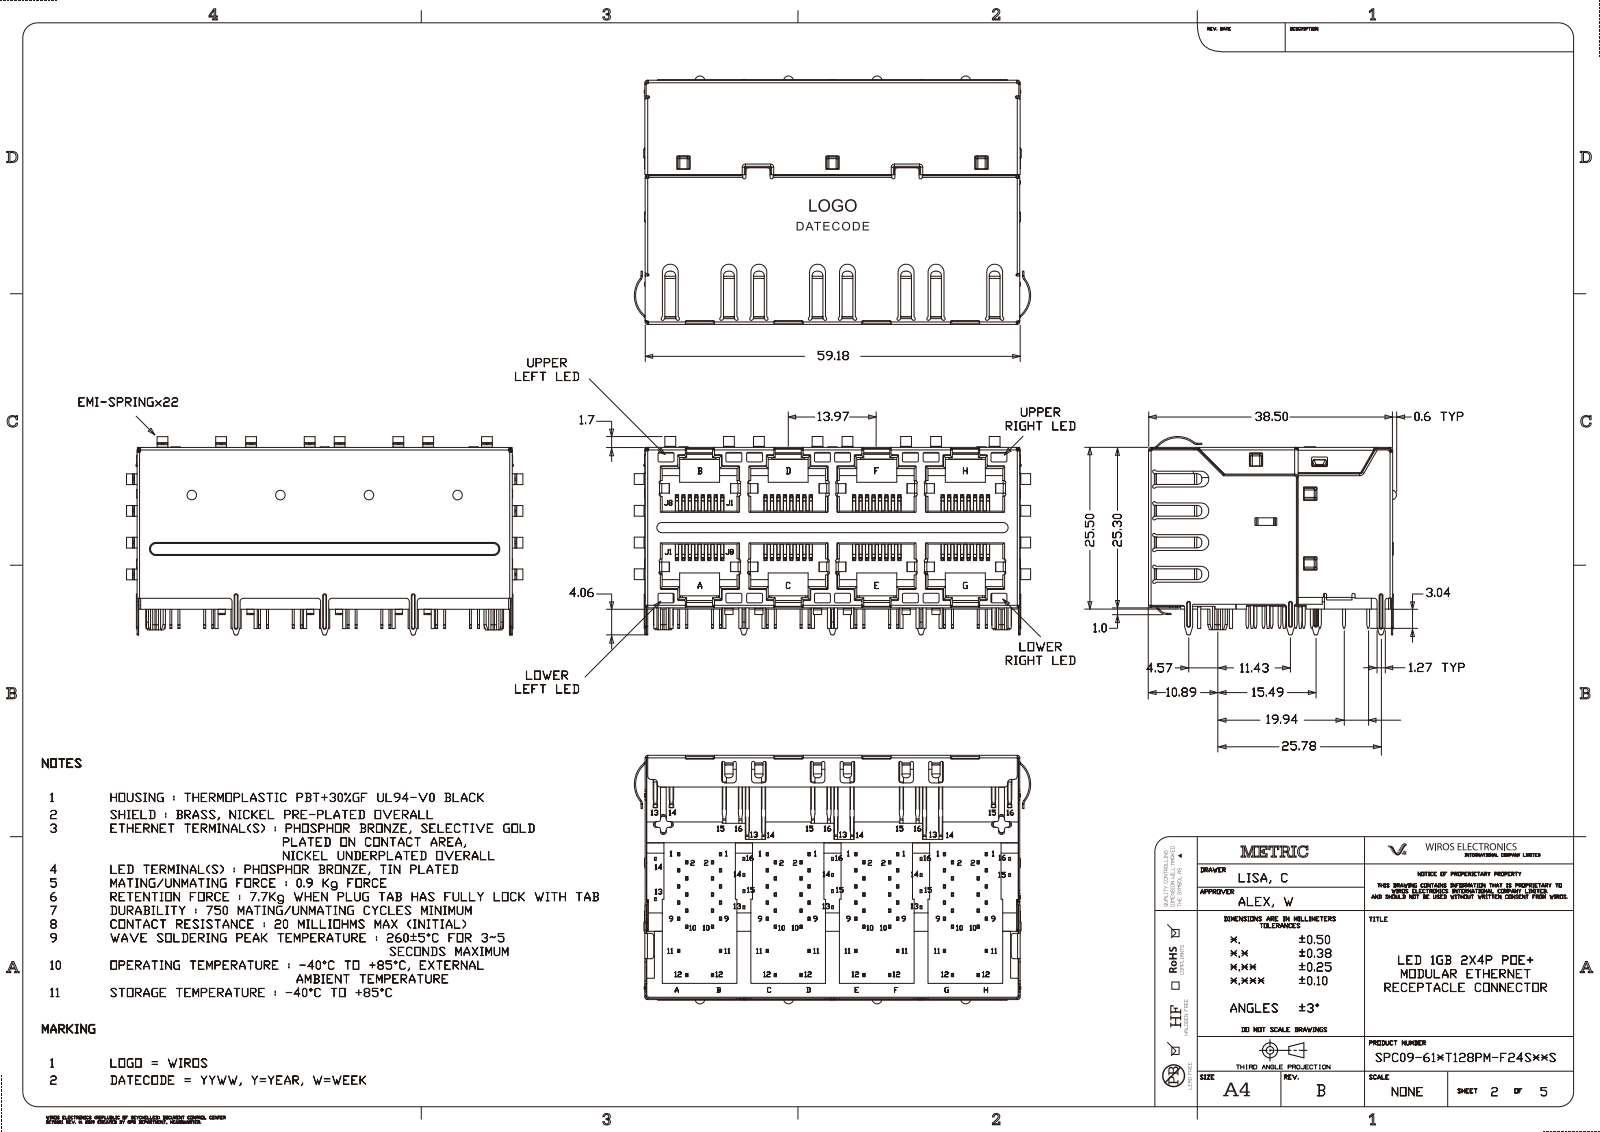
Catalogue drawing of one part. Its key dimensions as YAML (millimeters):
part_name: "RRMXX-DXXXX-XXXP（3D-20200612）实体"
step_written_by: "SolidWorks 2018 (CONFIG_CONTROL_DESIGN)"
units: millimeters
bodies: {solids: 5, faces: 2451, planar: 2074, cylindrical: 373, other: 4}
overall_size: [62.18, 38.6, 31.06]
volume: 49973
surface_area: 15357
partial_cylinders:
  - {radius: 0.2, count: 96}
  - {radius: 0.35, count: 40}
  - {radius: 0.3, count: 24}
  - {radius: 0.7, count: 23}
  - {radius: 0.5, count: 20}
  - {radius: 0.4, count: 9}
  - {radius: 9, count: 3}
  - {radius: 9.2, count: 3}
face_to_face_distances: [25.04, 59.18, 13.97, 10.05, 15.25, 38.5, 0.75, 27.94, 24.55, 9.3]
